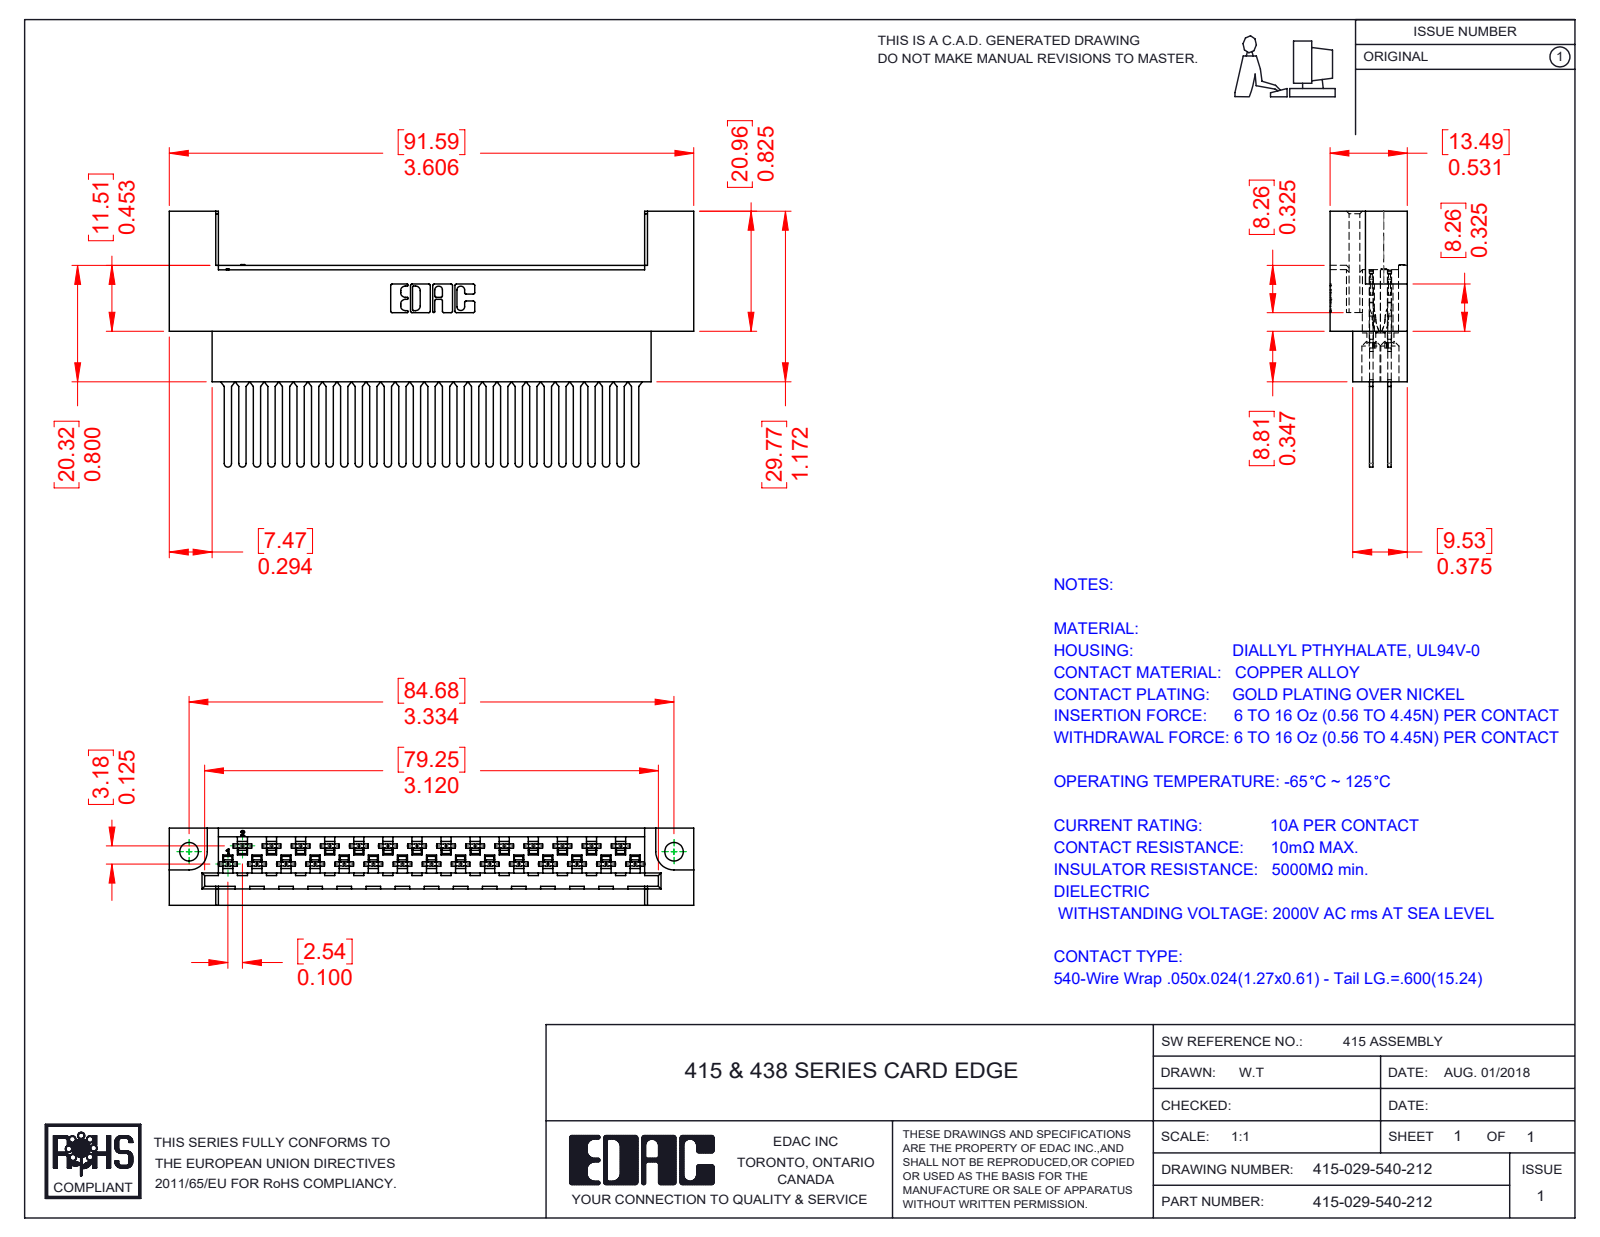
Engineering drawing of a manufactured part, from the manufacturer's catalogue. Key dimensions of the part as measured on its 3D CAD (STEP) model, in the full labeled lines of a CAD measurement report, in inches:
Part name (STEP PRODUCT): 516-290-001_540; 415-029-540-212; 415-210-001_415-210-029-212
STEP written by: SolidWorks 2016 (CONFIG_CONTROL_DESIGN)
Units: inches
Bodies: 30 solids, 3002 faces (1919 planar, 800 cylindrical, 283 other)
Overall size (bounding box): 3.606 × 1.758 × 0.531
Volume: 1.013 in³ · Surface area: 32.1 in²
Round holes (diameter × count): ⌀0.05 ×29, ⌀0.13 ×29, ⌀0.128 ×2
Partial cylindrical surfaces — rounded edges, fillets, slot ends (radius × count): R0.012 ×116, R0.022 ×116, R0.007 ×58, R0.008 ×58, R0.016 ×58, R0.08 ×58, R0.025 ×29, R0.01 ×22
Main face-to-face distances: 0.125, 0.024, 0.074, 0.295, 0.531, 0.05, 0.26, 0.271, 0.236, 0.111
Hole centre spacings: 0.2, 0.4, 0.6, 0.8, 1, 1.2, 1.4, 0.1
